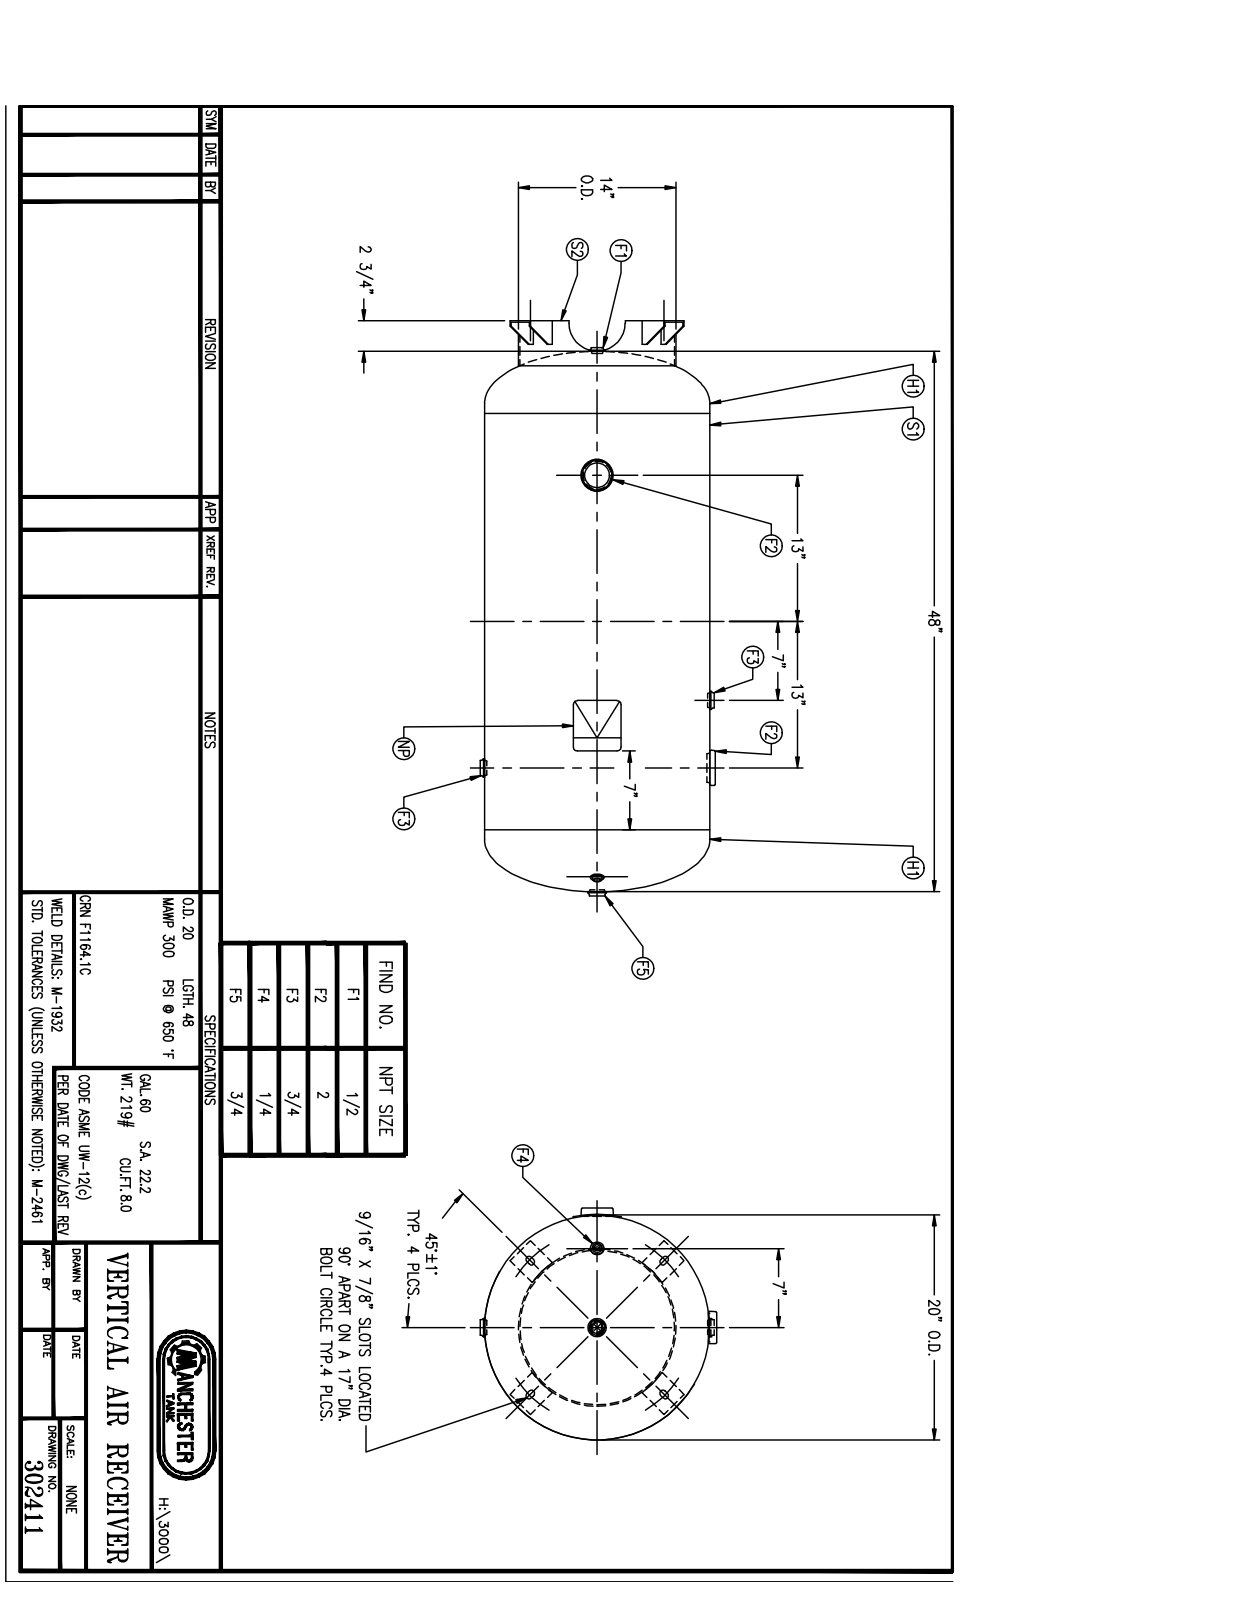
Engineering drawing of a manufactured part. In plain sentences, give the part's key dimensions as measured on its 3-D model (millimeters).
The part is named "302411". Its 3-D file was written by "SolidWorks 2011 (CONFIG_CONTROL_DESIGN)". It is 0 solids with 248 faces: 99 planar, 73 cylindrical and 76 other. Overall it measures 1301.4 by 544.8 by 529.1 millimeters. Round holes: 3 of diameter 26.7, 2 of diameter 60.3, 1 of diameter 13.7, 1 of diameter 21.3, 1 of diameter 25.4, 1 of diameter 350.3, 1 of diameter 496.5. Round bosses or shafts: 2 of diameter 92.1, 2 of diameter 52.4, 1 of diameter 508, 1 of diameter 495.3, 1 of diameter 355.6, 1 of diameter 52.4, 1 of diameter 46.1, 1 of diameter 38.1. Partial cylindrical surfaces (rounded edges, fillets, slot ends): 8 of radius 6.4, 8 of radius 7.1, 8 of radius 9.8, 1 of radius 255.5. The main face-to-face distances are 3.4, 3.4, 876.3, 60.6, 60.5, 3.3, 3.4, 3.6, 3.4, 57.2. The hole center spacings are 152.4.
